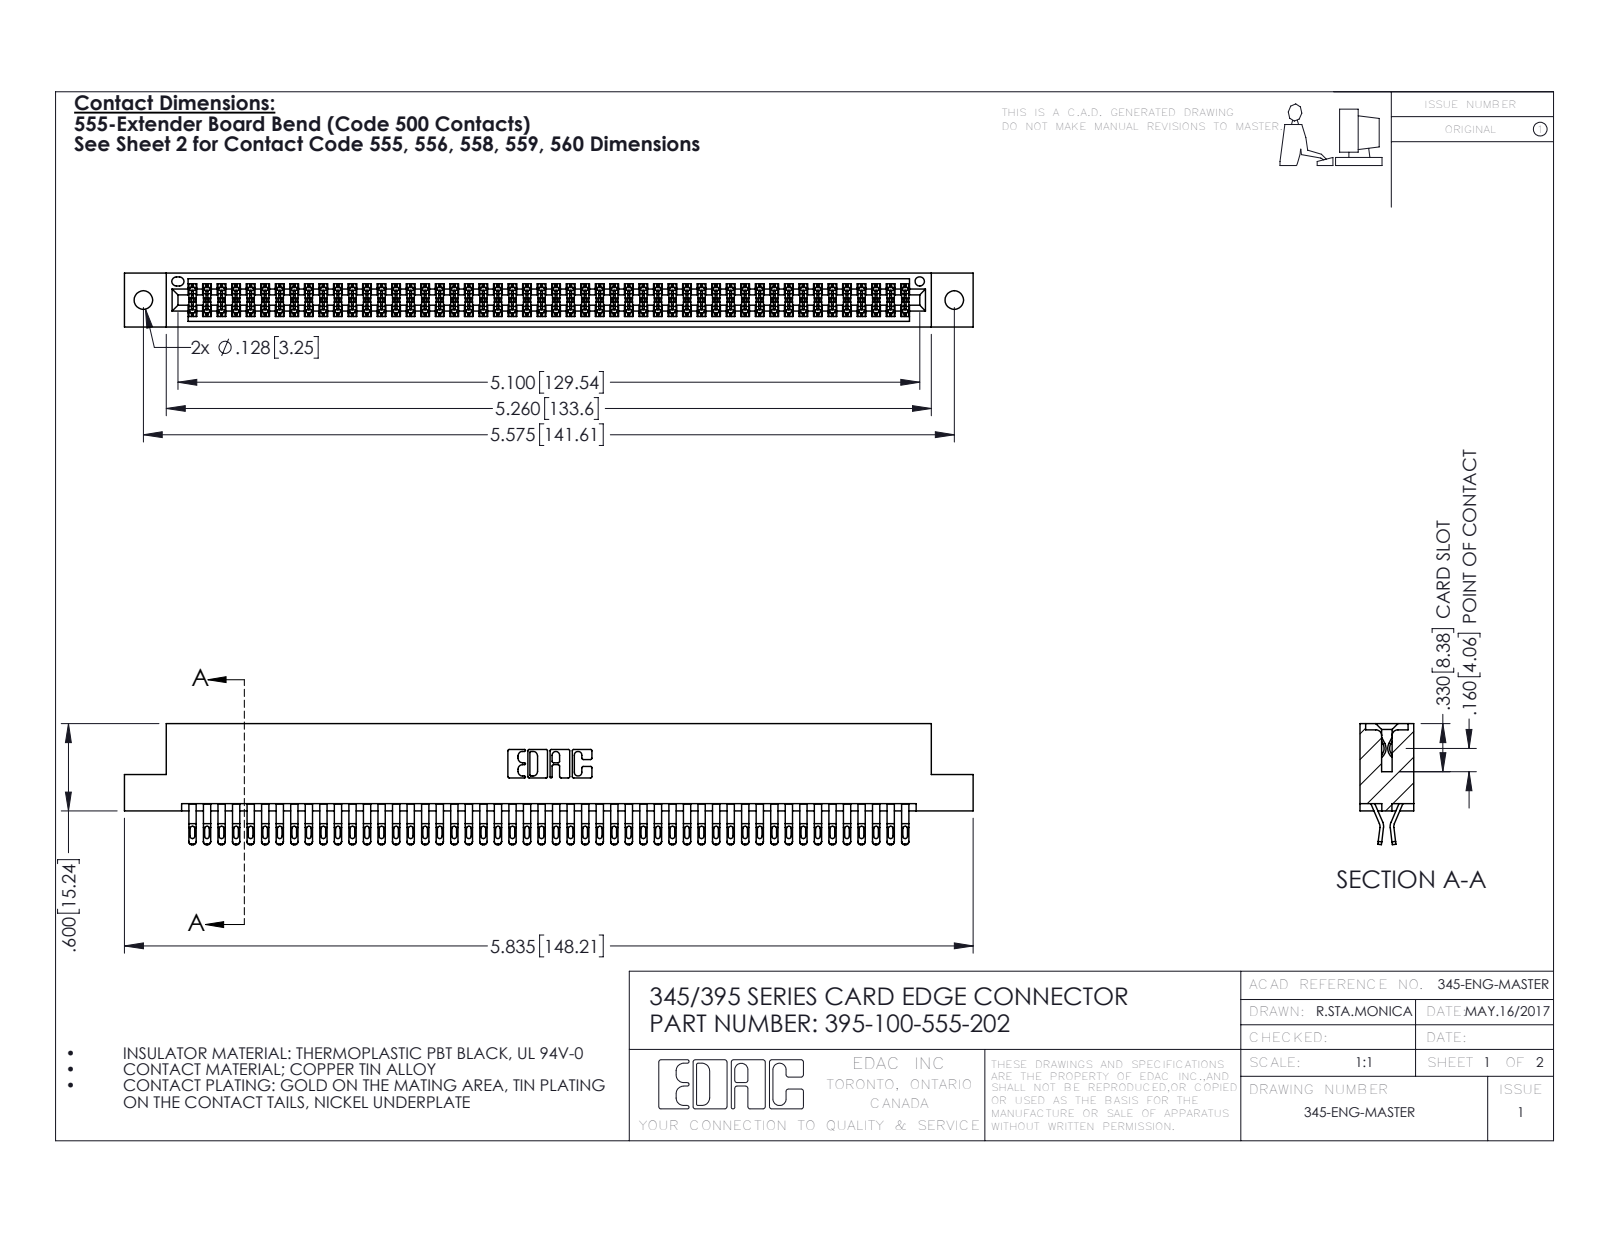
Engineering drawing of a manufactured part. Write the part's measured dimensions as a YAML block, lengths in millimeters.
part_name: "345 Part_Flush Mounting Lugs - 0.128 Dia; 345-292-001_555 Tail; 395-100-555-202"
step_written_by: "SolidWorks 2016 (CONFIG_CONTROL_DESIGN)"
units: millimeters
bodies: {solids: 101, faces: 5726, planar: 3180, cylindrical: 2546, other: 0}
overall_size: [148.2, 21.1, 9.4]
volume: 14700
surface_area: 22660
round_holes:
  - {diameter: 3.3, count: 2}
  - {diameter: 1.6, count: 1}
partial_cylinders:
  - {radius: 0.4, count: 250}
  - {radius: 0.5, count: 200}
  - {radius: 0.2, count: 150}
  - {radius: 0.3, count: 22}
  - {radius: 0.2, count: 6}
  - {radius: 0.8, count: 6}
  - {radius: 0.7, count: 3}
  - {radius: 0.3, count: 2}
face_to_face_distances: [7.6, 1.8, 0.6, 9.4, 5.1, 2.5, 6.9, 5.7, 4.4, 3.8]
hole_center_spacings: [6.9, 135.6, 141.6]
